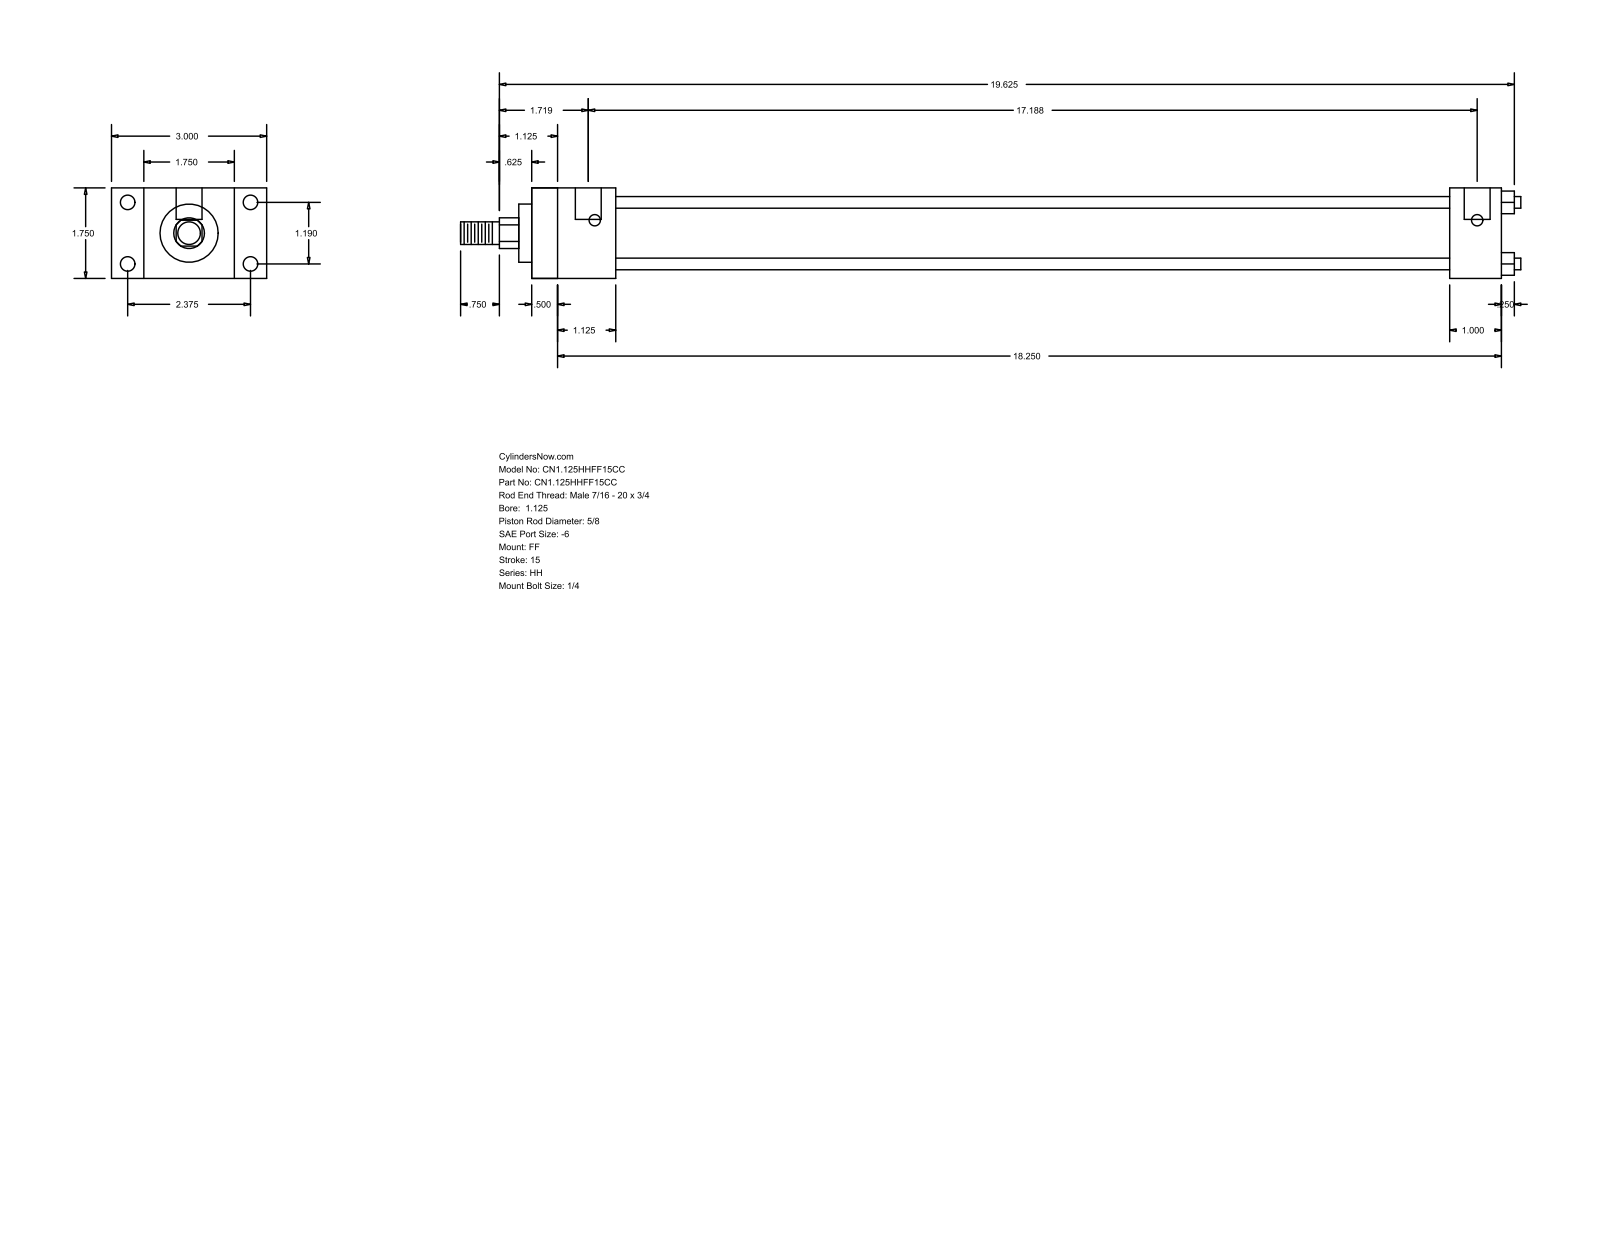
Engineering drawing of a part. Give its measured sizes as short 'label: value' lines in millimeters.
name: HH_FF__0112_0.625
written by: GSSL Pune (CONFIG_CONTROL_DESIGN)
unit: mm
bodies: 0 solids, 92 faces (64 planar, 28 cylindrical, 0 other)
size: 520.7 × 76.2 × 44.45
holes: 4× ⌀5.56, 4× ⌀7.14, 2× ⌀12.7
bosses: 4× ⌀5.71, 1× ⌀34.92, 1× ⌀28.57, 1× ⌀15.88, 1× ⌀11.11
rounds: 1× R7.54
face distances: 44.46, 476.24, 12.69, 463.55, 15.87, 28.58, 60.33, 41.27, 450.85, 438.16
hole spacings: 30.22, 60.32, 67.47, 433.39, 3.17, 436.56
